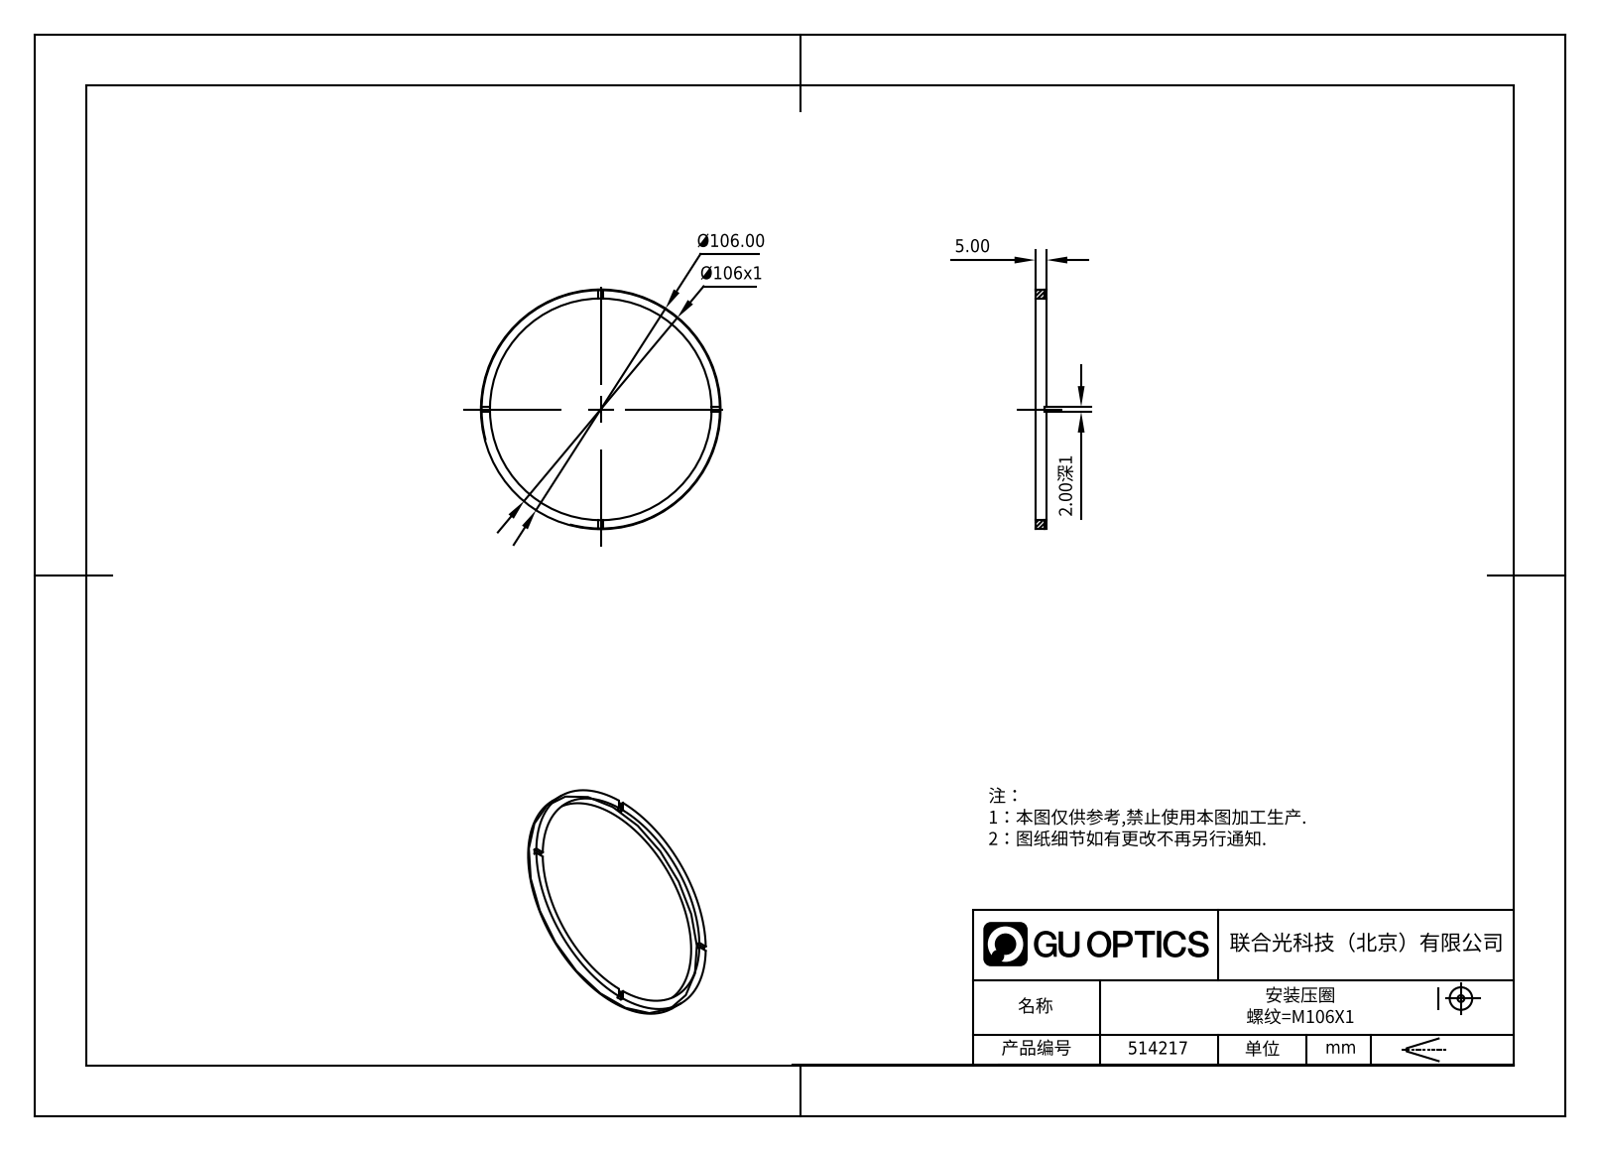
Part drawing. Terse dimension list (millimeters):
name: 514217
written by: SolidWorks 2020 (CONFIG_CONTROL_DESIGN)
unit: mm
bodies: 1 solid, 21 faces (17 planar, 4 cylindrical, 0 other)
size: 106 × 106 × 5
volume: 6 377 mm³; area: 5 784 mm²
holes: 1× ⌀98
bosses: 1× ⌀106
face distances: 5, 4, 1, 2
